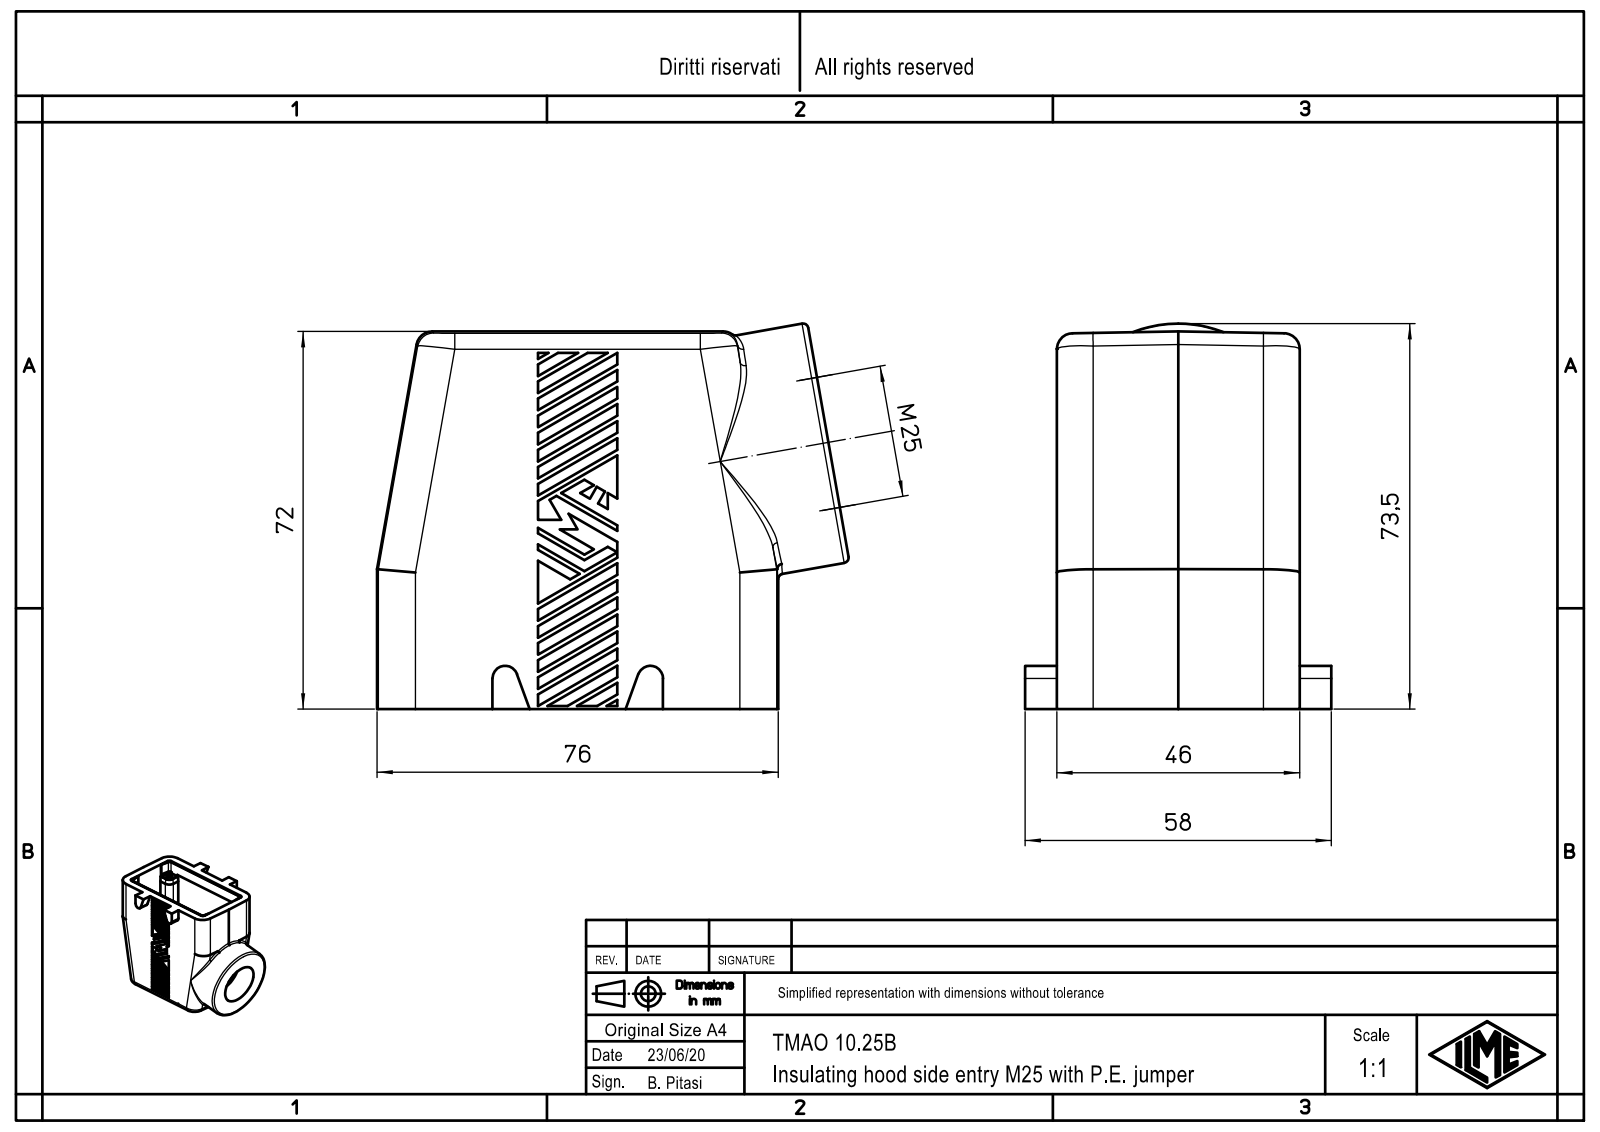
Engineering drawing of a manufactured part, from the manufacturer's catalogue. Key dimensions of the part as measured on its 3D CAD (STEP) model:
Part name (STEP PRODUCT): TMAO_10.25B
STEP written by: Creo Elements/Direct Modeling 20.1B 02-Apr-2019 (C) Parametric Technology GmbH (AUTOMOTIVE_DESIGN)
Units: millimetres
Bodies: 1 solid, 571 faces (402 planar, 83 cylindrical, 86 other)
Overall size (bounding box): 89.33 × 72.98 × 58
Volume: 119 133 mm³ · Surface area: 41 219 mm²
Round holes (diameter × count): ⌀3 ×4, ⌀3.5 ×4, ⌀21 ×1, ⌀25 ×1
Round bosses / shafts (diameter × count): ⌀4.8 ×4, ⌀46 ×1
Partial cylindrical surfaces — rounded edges, fillets, slot ends (radius × count): R1.5 ×12, R7 ×8, R3 ×6, R1.3 ×4, R1.6 ×4, R2 ×4, R3.5 ×4, R2.4 ×2
Main face-to-face distances: 46, 65.99, 0.5, 45.5, 5.6, 6.1, 5.3, 26.51, 5.8, 40.2
Hole centre spacings: 27, 57, 63.07
